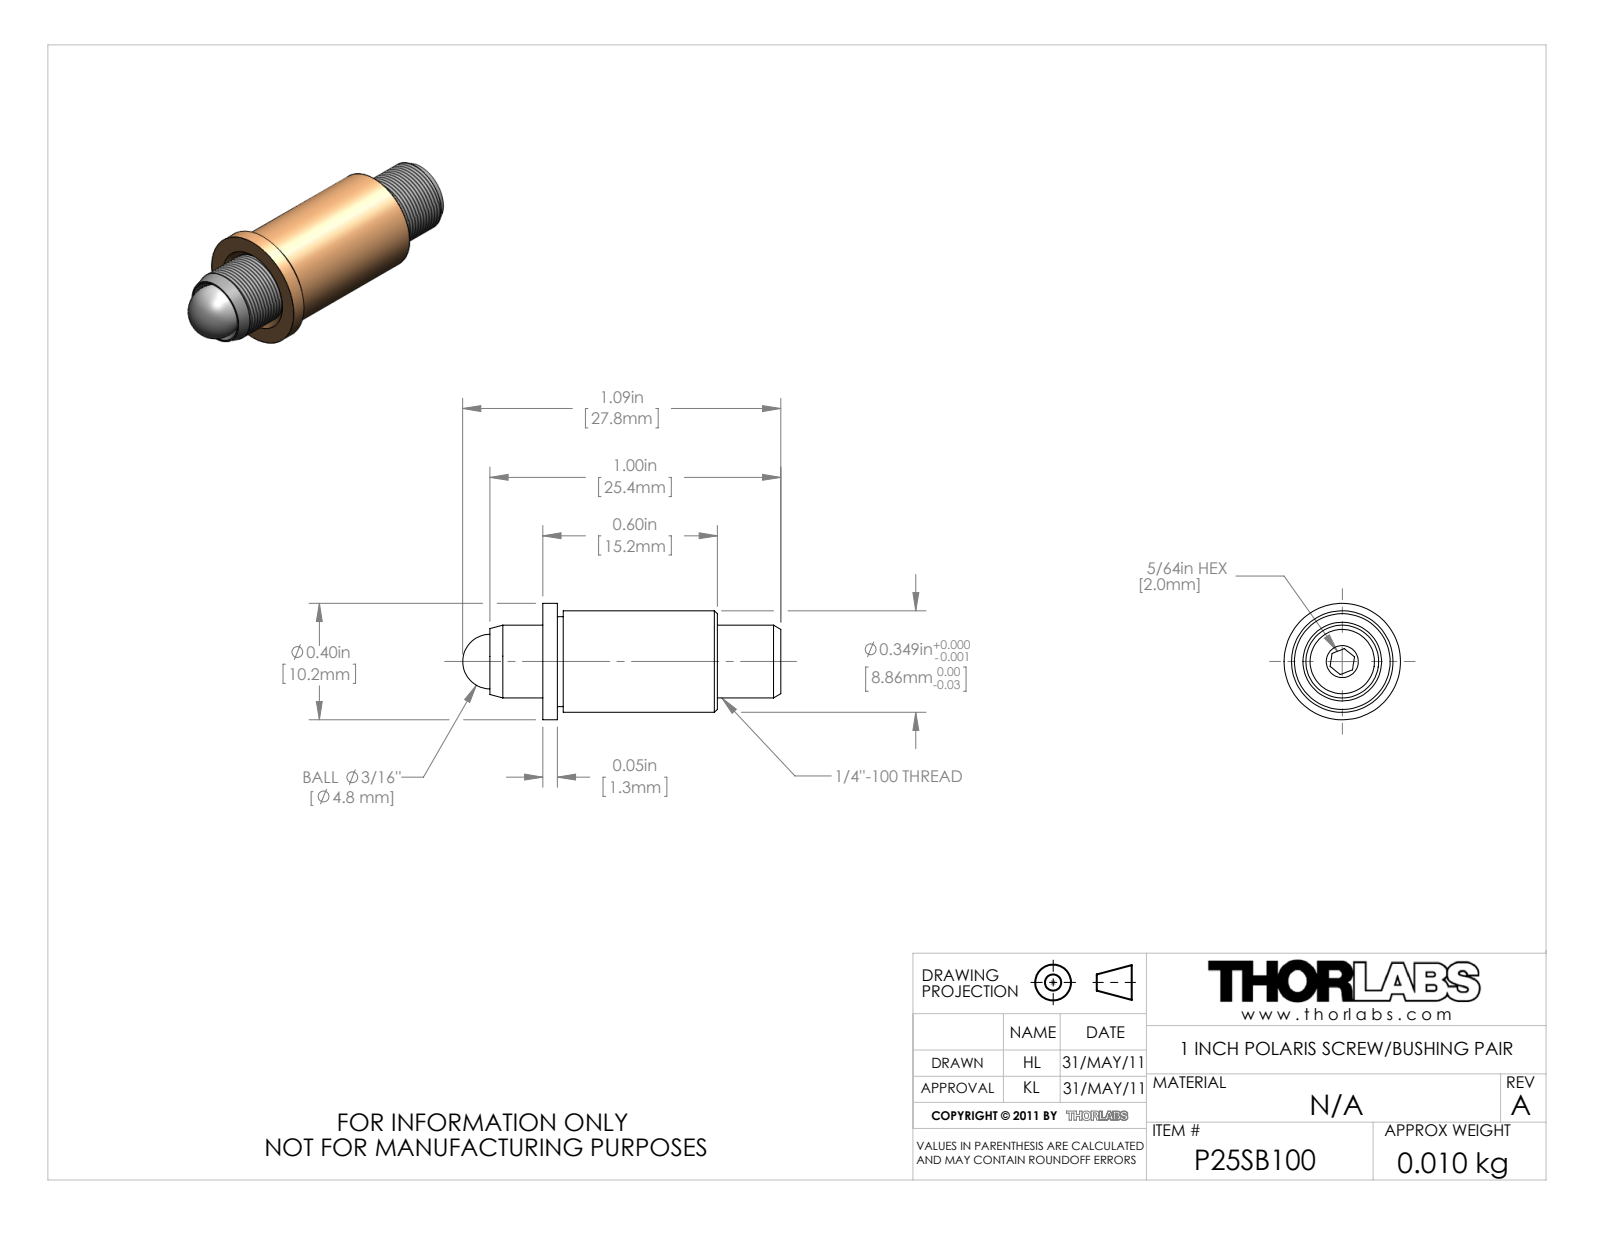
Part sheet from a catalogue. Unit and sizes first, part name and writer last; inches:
Units: inches
Overall size (bounding box): 1.094 × 0.4 × 0.4
Round holes (diameter × count): ⌀0.25 ×1
Round bosses / shafts (diameter × count): ⌀0.4 ×1, ⌀0.349 ×1, ⌀0.309 ×1
Main face-to-face distances: 0.05, 0.819, 0.769, 0.6, 0.55, 0.219, 0.07, 0.02, 0.53, 0.748
Volume: 0.078 in³ · Surface area: 2.357 in²
Bodies: 3 solids, 48 faces (18 planar, 10 cylindrical, 20 other)
Part name (STEP PRODUCT): 22539-E0W
STEP written by: SolidWorks 2011 (CONFIG_CONTROL_DESIGN)
